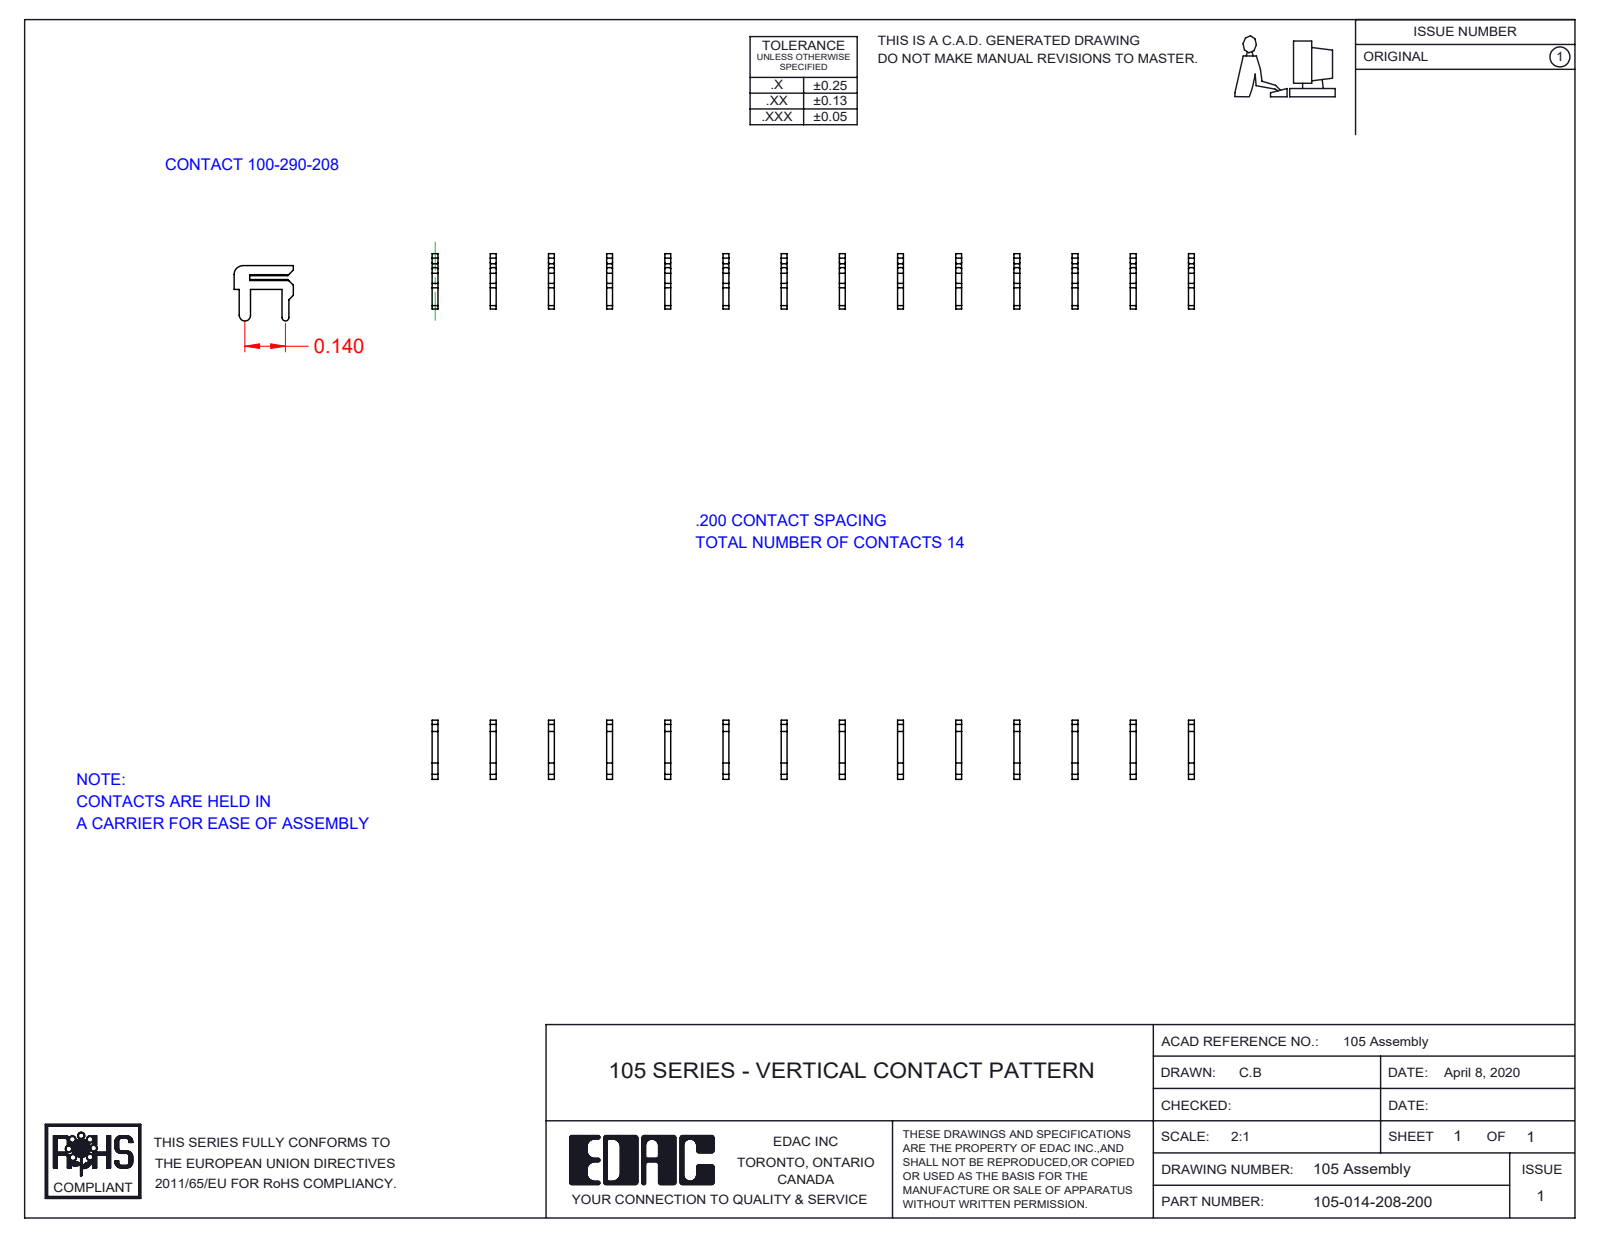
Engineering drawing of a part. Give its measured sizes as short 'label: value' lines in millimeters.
name: 100-290-001_100-290-208; 105-014-208-200
written by: SolidWorks 2016 (CONFIG_CONTROL_DESIGN)
unit: mm
bodies: 14 solids, 350 faces (308 planar, 42 cylindrical, 0 other)
size: 66.5 × 5.2 × 4.8
volume: 100 mm³; area: 595 mm²
rounds: 1× R0.3, 1× R0.5, 1× R0.8
face distances: 5.1, 10.2, 15.2, 20.3, 25.4, 30.5, 35.6, 40.6, 0.5, 5.6
